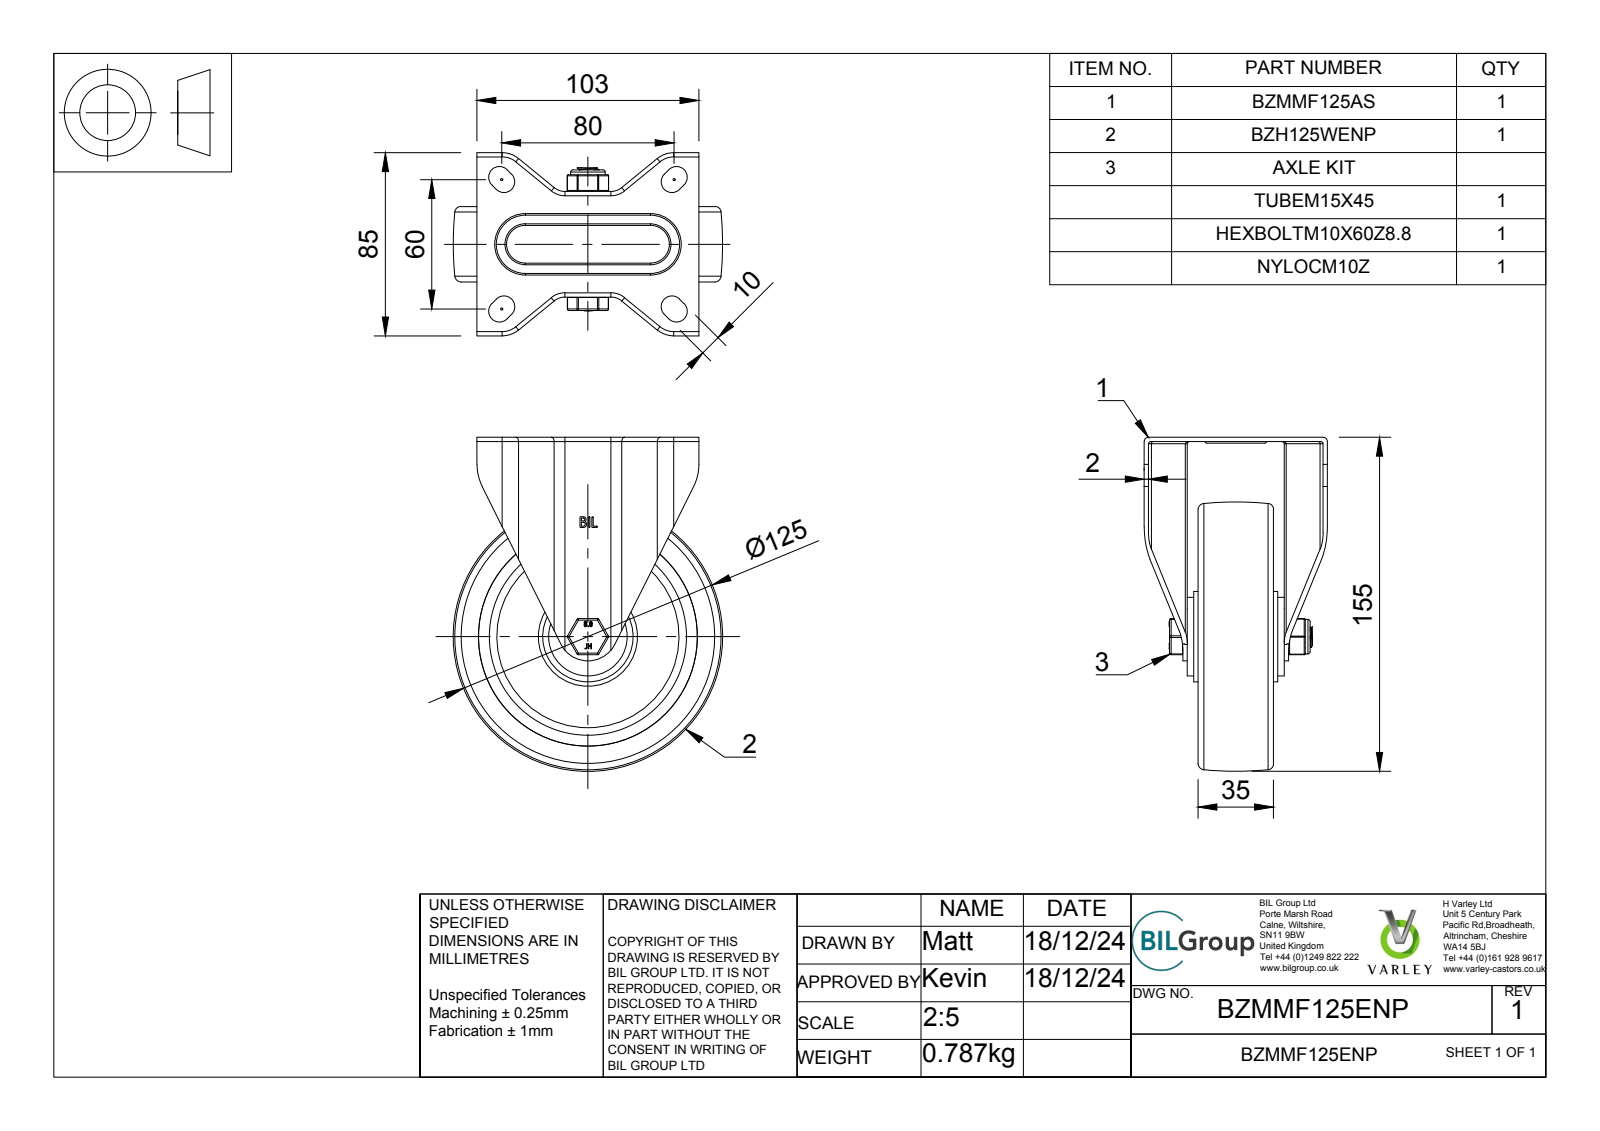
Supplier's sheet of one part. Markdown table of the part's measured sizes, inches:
| quantity | value |
| --- | --- |
| part name | BZMMF125ENP v4; BZMMF125AS v1; BZMMF125AS; ZINC PLATED, PRESSED STEEL BRACKET (+8 more) |
| STEP written by | Autodesk Translation Framework v13.20.0.188 (AP242_MANAGED_MODEL_BASED_3D_ENGINEERING_MIM_LF) |
| units | inches |
| bodies | 7 solids, 393 faces (138 planar, 151 cylindrical, 104 other) |
| overall size | 6.102 × 4.921 × 3.346 |
| volume | 20.81 in³ |
| surface area | 195.2 in² |
| round holes (diameter × count) | 0.394 × 1, 0.402 × 1, 0.472 × 1, 0.606 × 1, 3.602 × 1, 3.996 × 1 |
| round bosses / shafts (diameter × count) | 1.654 × 1, 1.437 × 1, 0.63 × 1, 0.61 × 1, 0.589 × 1, 0.388 × 1, 0.32 × 1 |
| partial cylindrical surfaces (radius × count) | 0.03 × 20, 0.02 × 18, 0.039 × 8, 0.079 × 8, 0.197 × 8, 0.157 × 4, 0.236 × 4, 0.315 × 4 |
| main face-to-face distances | 0.079, 0.541, 0.837, 0.197, 0.738, 1.033, 1.575, 0.742, 1.654, 0.276 |
